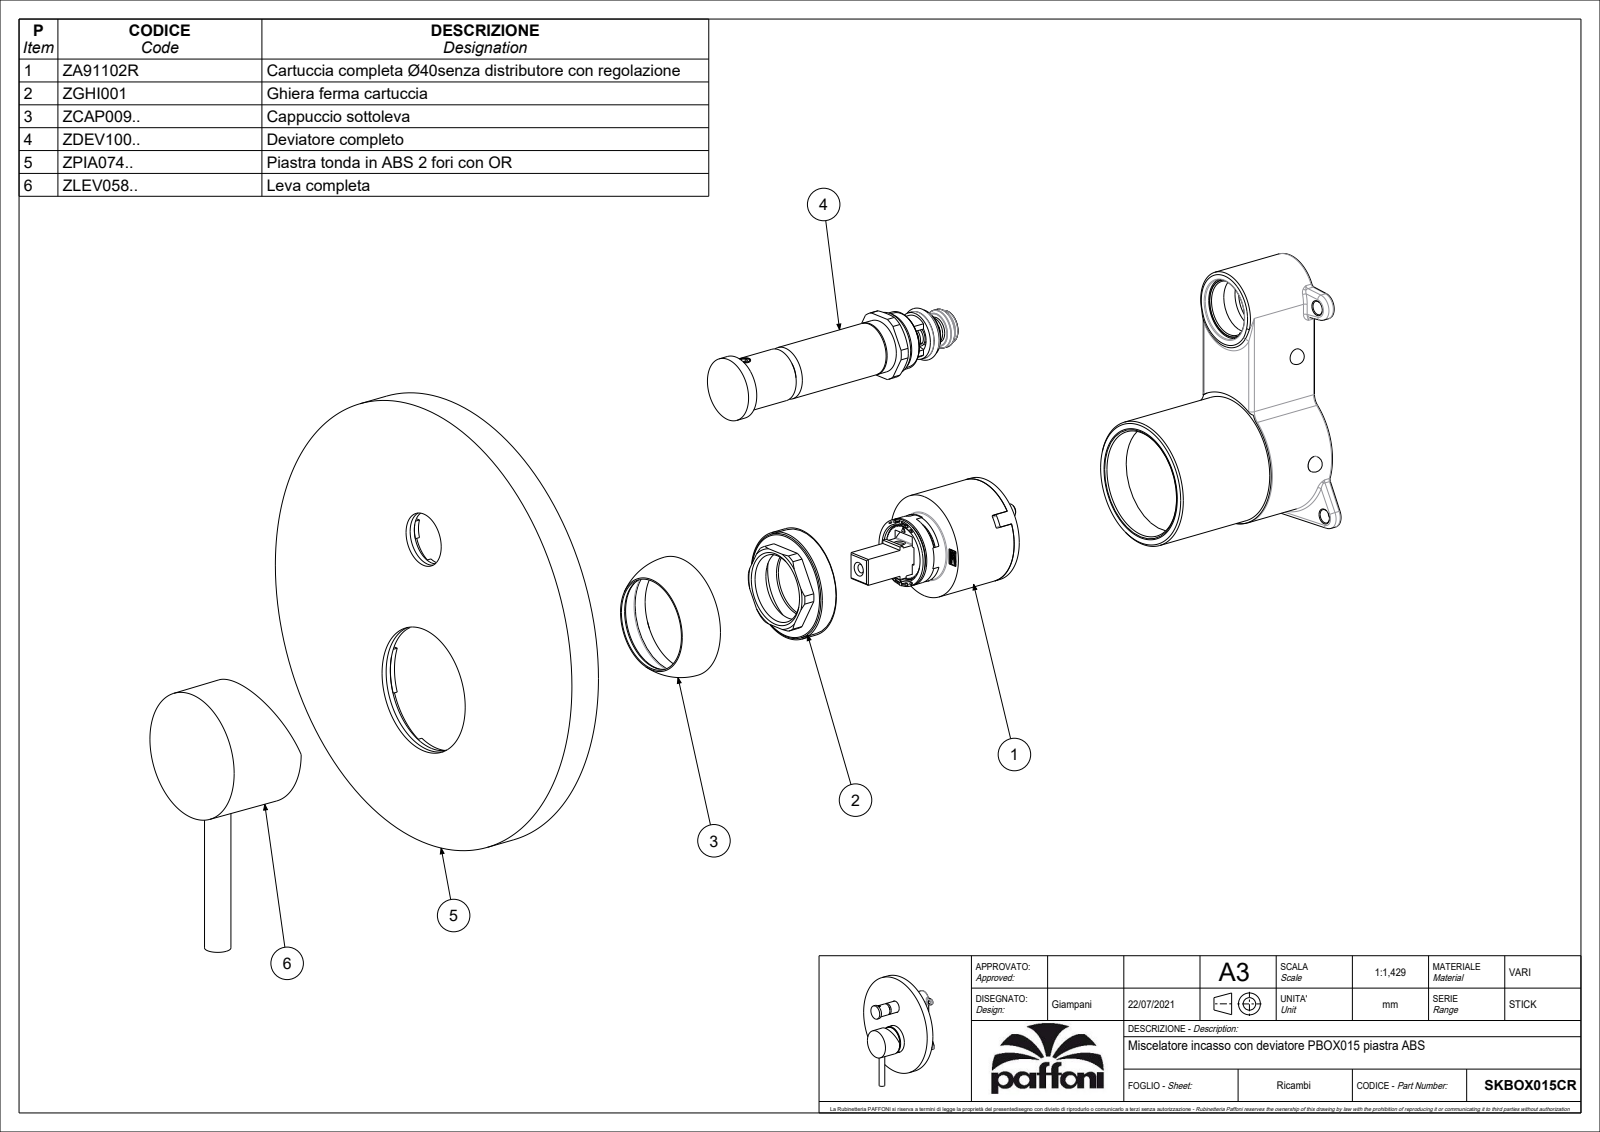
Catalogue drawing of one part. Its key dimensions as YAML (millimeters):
part_name: "SKBOX015CR"
step_written_by: "CREO PARAMETRIC BY PTC INC, 2020044 (CONFIG_CONTROL_DESIGN)"
units: millimeters
bodies: {solids: 2, faces: 142, planar: 45, cylindrical: 55, other: 42}
overall_size: [202.12, 173, 69.8]
volume: 368867
surface_area: 83232
round_holes:
  - {diameter: 4.2, count: 1}
  - {diameter: 4.5, count: 1}
  - {diameter: 5.5, count: 1}
  - {diameter: 6, count: 1}
  - {diameter: 12, count: 1}
  - {diameter: 35, count: 1}
  - {diameter: 40, count: 1}
  - {diameter: 40.5, count: 1}
  - {diameter: 40.7, count: 1}
  - {diameter: 48, count: 1}
round_bosses_or_shafts:
  - {diameter: 20, count: 2}
  - {diameter: 173, count: 1}
  - {diameter: 50, count: 1}
  - {diameter: 48.1, count: 1}
  - {diameter: 24, count: 1}
  - {diameter: 15, count: 1}
  - {diameter: 12, count: 1}
  - {diameter: 8, count: 1}
partial_cylinders:
  - {radius: 3.9, count: 1}
  - {radius: 13.3, count: 1}
face_to_face_distances: [13, 62.8, 49.8, 51.8, 38.8, 11, 44, 31, 7.8, 18.8]
hole_center_spacings: [1.47, 1.6, 13.3]
